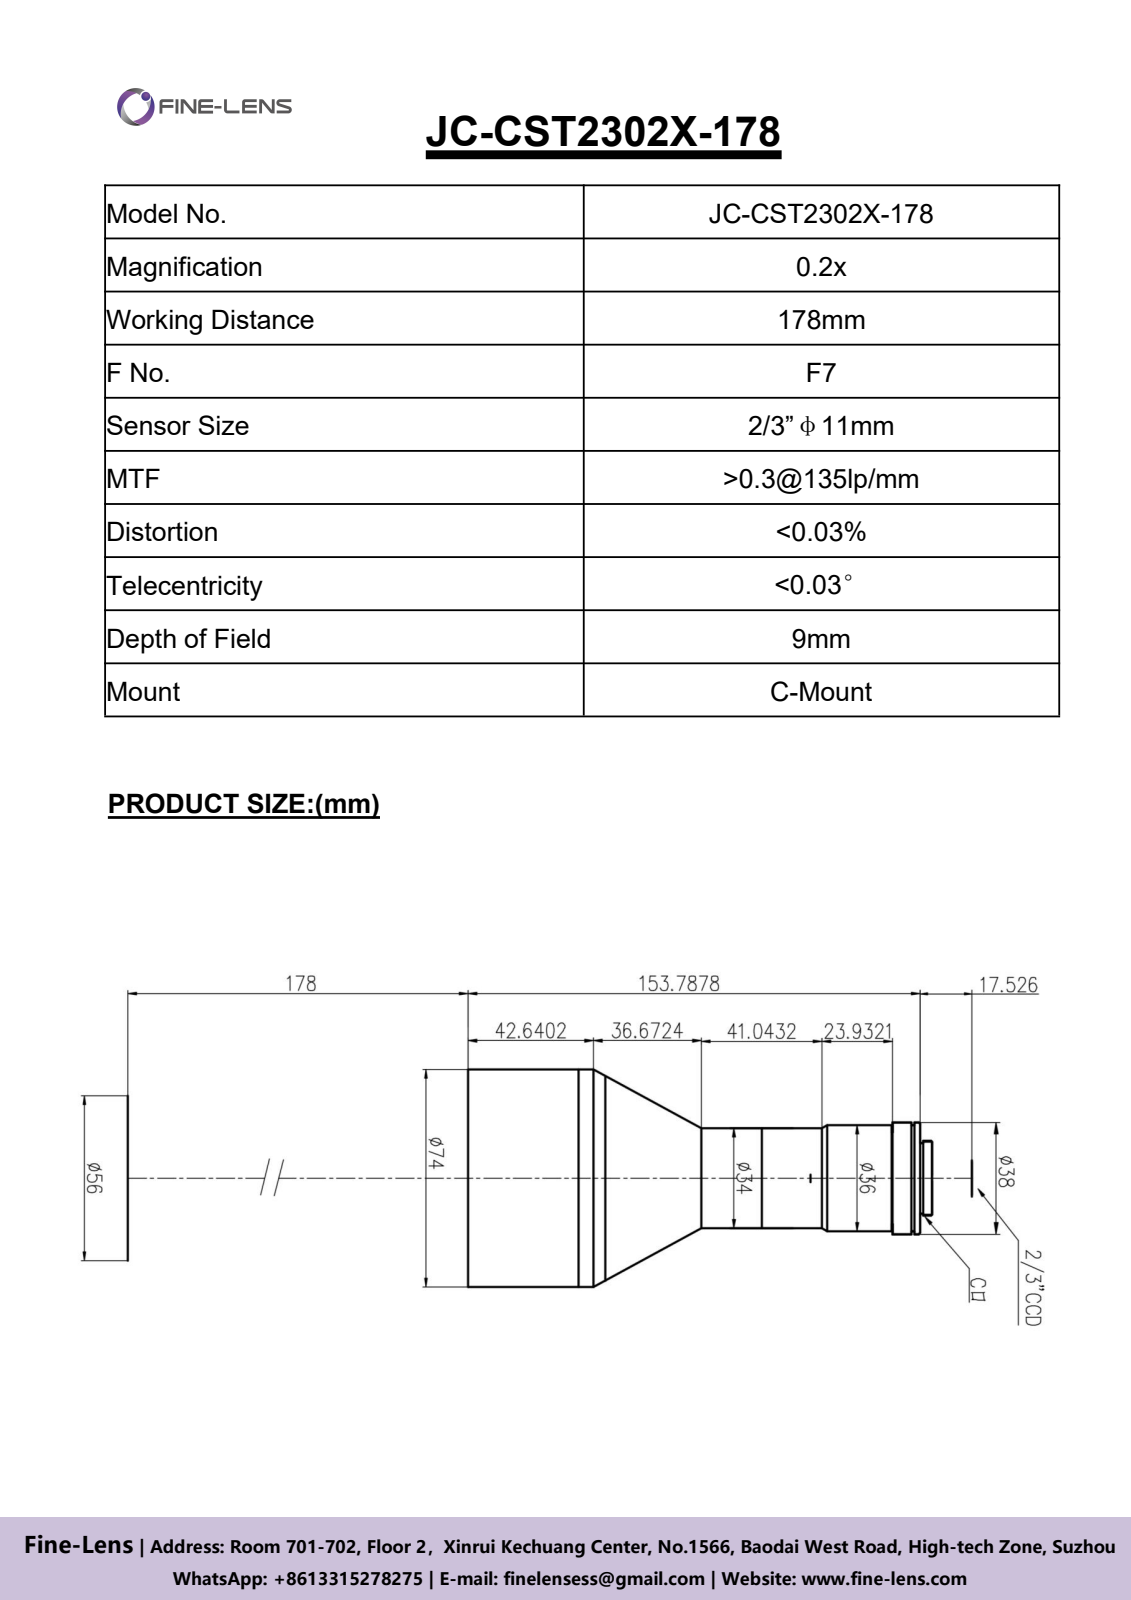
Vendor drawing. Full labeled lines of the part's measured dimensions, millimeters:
Part name (STEP PRODUCT): WT-5M02-178.
STEP written by: SolidWorks 2016 (CONFIG_CONTROL_DESIGN)
Units: millimetres
Bodies: 1 solid, 35 faces (9 planar, 20 cylindrical, 6 other)
Overall size (bounding box): 157.79 × 74.1 × 74.1
Volume: 195 488 mm³ · Surface area: 43 547 mm²
Round holes (diameter × count): ⌀15 ×1, ⌀65 ×1
Round bosses / shafts (diameter × count): ⌀74.1 ×1, ⌀74 ×1, ⌀38 ×1, ⌀36.71 ×1, ⌀36 ×1, ⌀34 ×1, ⌀30 ×1
Main face-to-face distances: 35, 157.79, 122.79, 153.79, 118.79, 4, 140.22, 105.22, 13.57, 17.57
